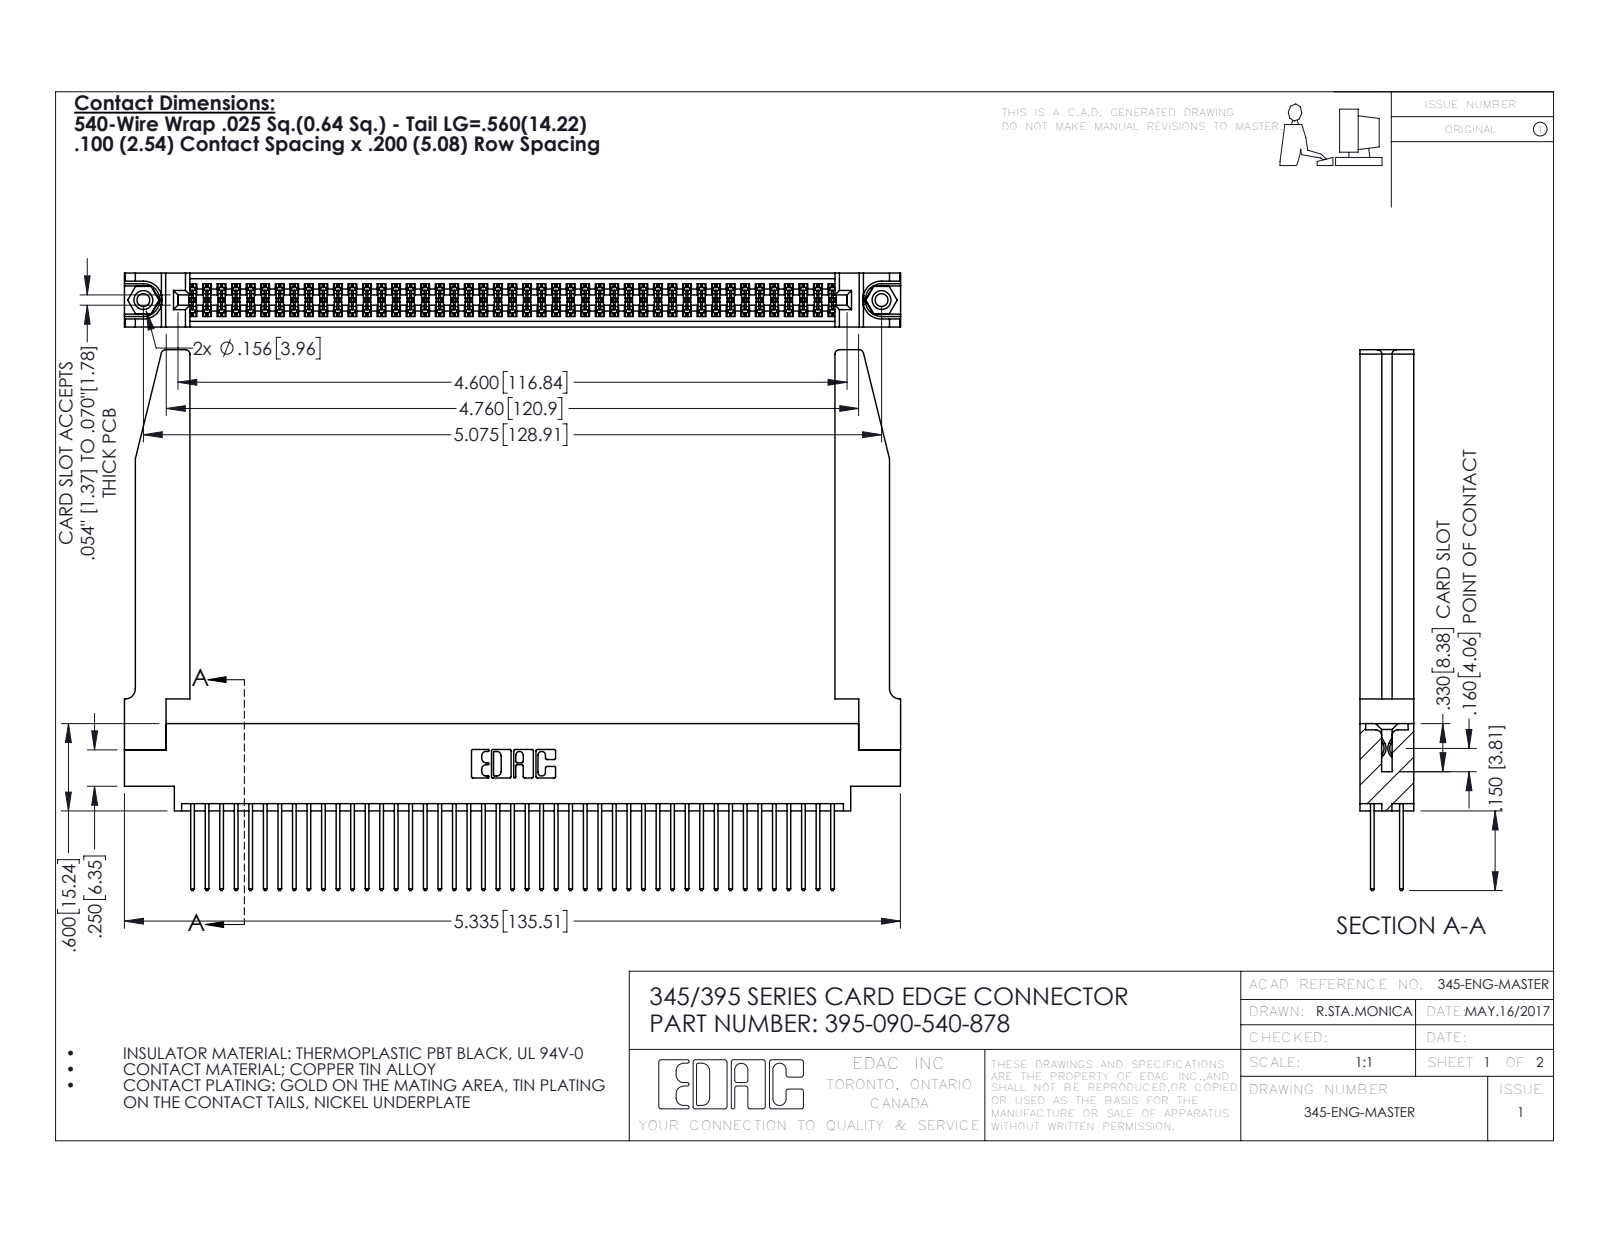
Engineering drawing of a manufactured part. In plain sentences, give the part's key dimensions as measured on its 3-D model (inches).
The part is named "345 Part_0.170 Offset - 0.156 Dia-TH; 345-250-001_345-250-001-102; 395-090-540-878; 345-220-078_345-220-078 (+1 more)". Its 3-D file was written by "SolidWorks 2016 (CONFIG_CONTROL_DESIGN)". It is 95 solids with 4864 faces: 3196 planar, 1616 cylindrical and 52 other. Overall it measures 5.336 by 3.717 by 0.37 inches. Its volume is 1.293 cubic inches and its surface area 44.12 square inches. Round holes: 2 of diameter 0.089, 2 of diameter 0.125, 2 of diameter 0.156, 1 of diameter 0.064. Round bosses or shafts: 2 of diameter 0.155. Partial cylindrical surfaces (rounded edges, fillets, slot ends): 135 of radius 0.006, 90 of radius 0.01, 22 of radius 0.01, 8 of radius 0.03, 6 of radius 0.007, 6 of radius 0.031, 3 of radius 0.026, 2 of radius 0.014. The main face-to-face distances are 0.072, 0.298, 0.37, 0.098, 0.272, 0.025, 0.2, 0.225, 0.175, 0.148. The hole center spacings are 0.27, 4.839, 5.075.
